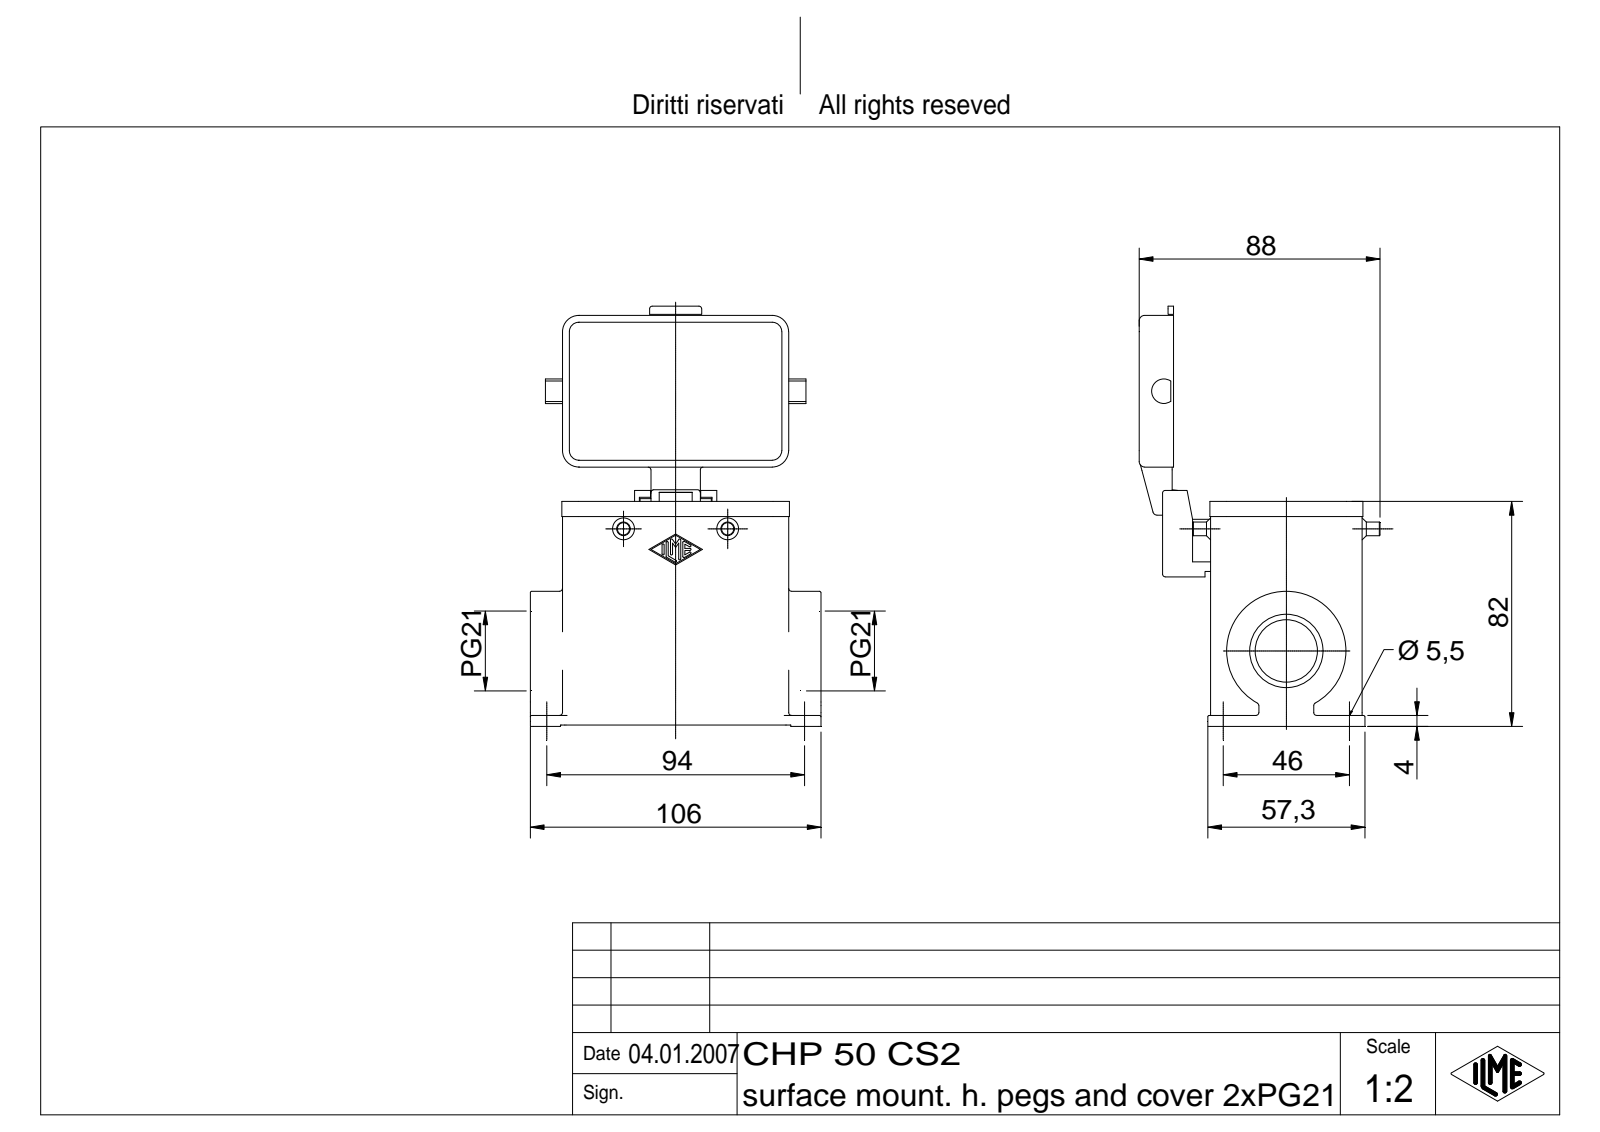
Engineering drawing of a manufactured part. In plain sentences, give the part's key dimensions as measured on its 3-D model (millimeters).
The part is named "CHP 50 CS2". Its 3-D file was written by "Autodesk Inventor 7 (AUTOMOTIVE_DESIGN)". It is 3 solids with 608 faces: 180 planar, 239 cylindrical and 189 other. Overall it measures 153.15 by 106 by 87.8 millimeters. Its volume is 171 148 cubic millimeters and its surface area 79 988 square millimeters. Round holes: 4 of diameter 2.46, 4 of diameter 3.1, 2 of diameter 5.5, 1 of diameter 4, 1 of diameter 22.78, 1 of diameter 26.78. Round bosses or shafts: 3 of diameter 5, 2 of diameter 3, 1 of diameter 43.5, 1 of diameter 7, 1 of diameter 4. Partial cylindrical surfaces (rounded edges, fillets, slot ends): 38 of radius 1, 17 of radius 0.5, 14 of radius 0.38, 12 of radius 6, 8 of radius 2, 5 of radius 1.5, 4 of radius 3, 4 of radius 3.5. The main face-to-face distances are 3, 52.3, 3.5, 55.3, 22.5, 49.3, 26, 81.3, 78.3, 29. The hole center spacings are 16, 66, 67.91, 14.32, 23.6, 30.41, 45.22, 80.06.
